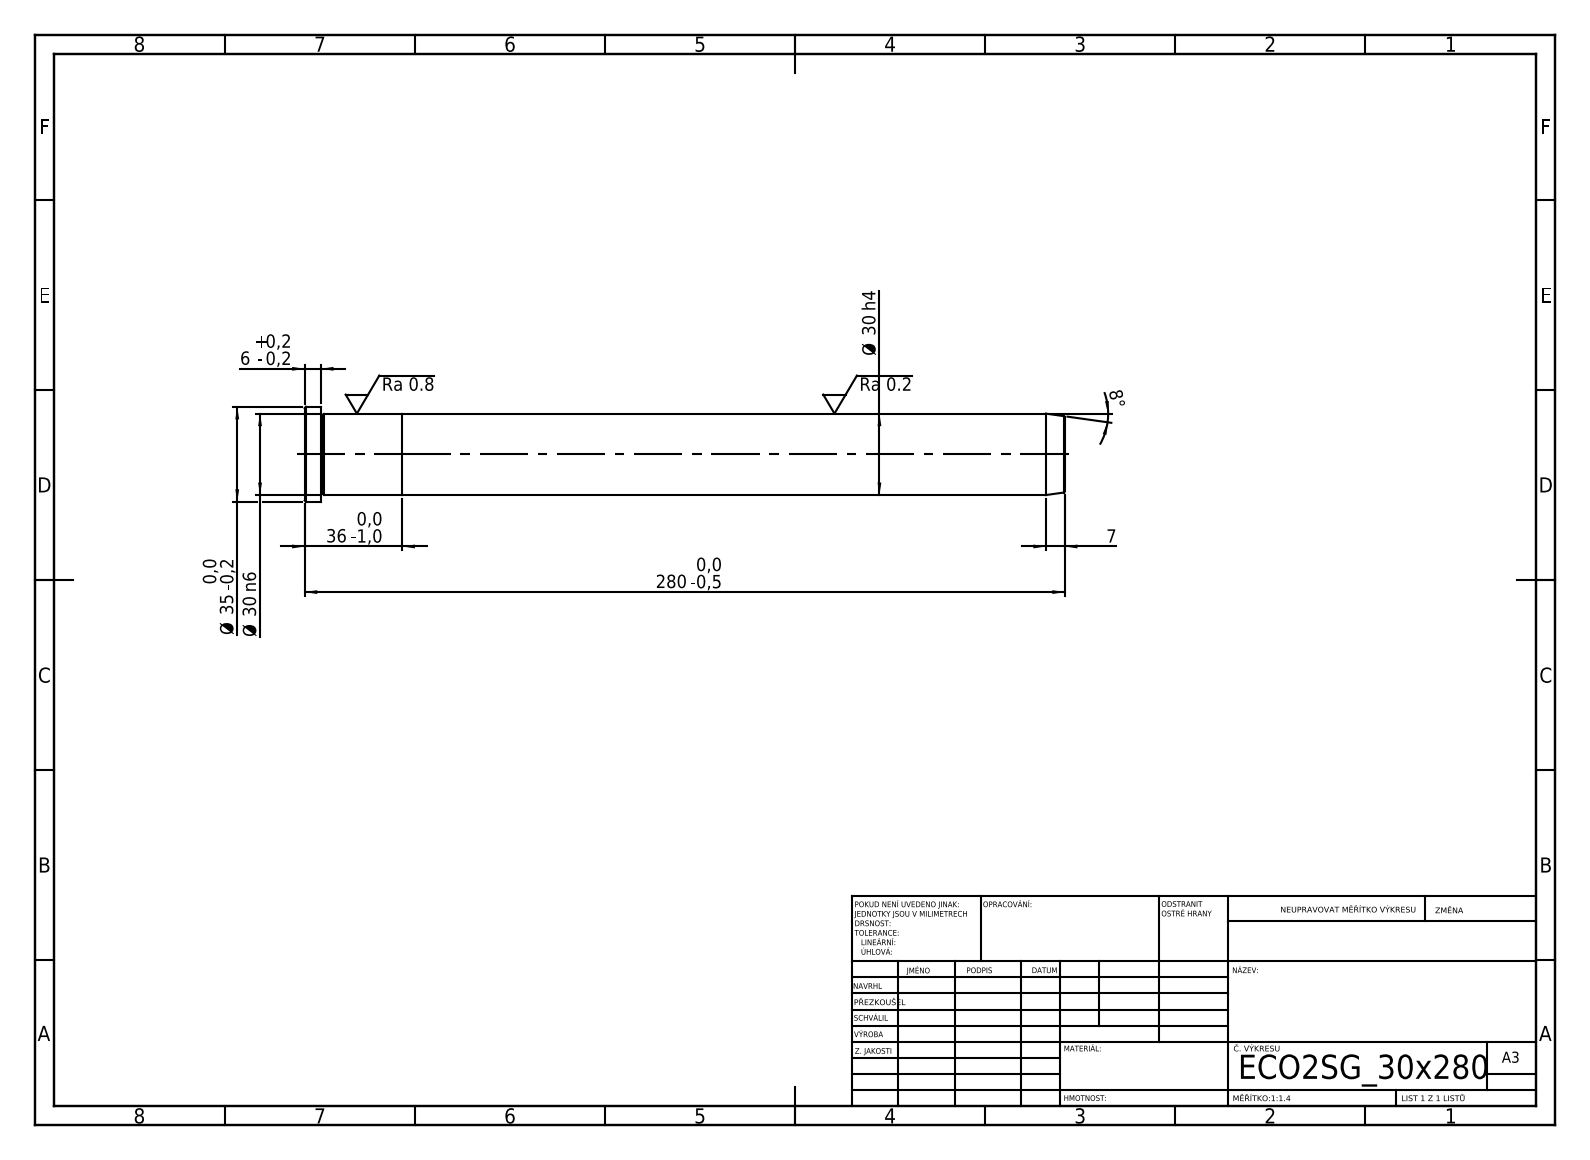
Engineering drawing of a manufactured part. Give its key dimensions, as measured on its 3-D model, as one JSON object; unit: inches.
{"step_written_by": "SolidWorks 2019 (CONFIG_CONTROL_DESIGN)", "units": "inches", "bodies": {"solids": 2, "faces": 21, "planar": 5, "cylindrical": 6, "other": 10}, "overall_size": [11.024, 1.378, 1.378], "volume_in3": 12.15, "surface_area_in2": 46.07, "round_bosses_or_shafts": [[1.378, 1], [1.181, 1]], "face_to_face_distances": [1.417, 9.606, 11.024, 10.787, 1.181, 0.236]}
